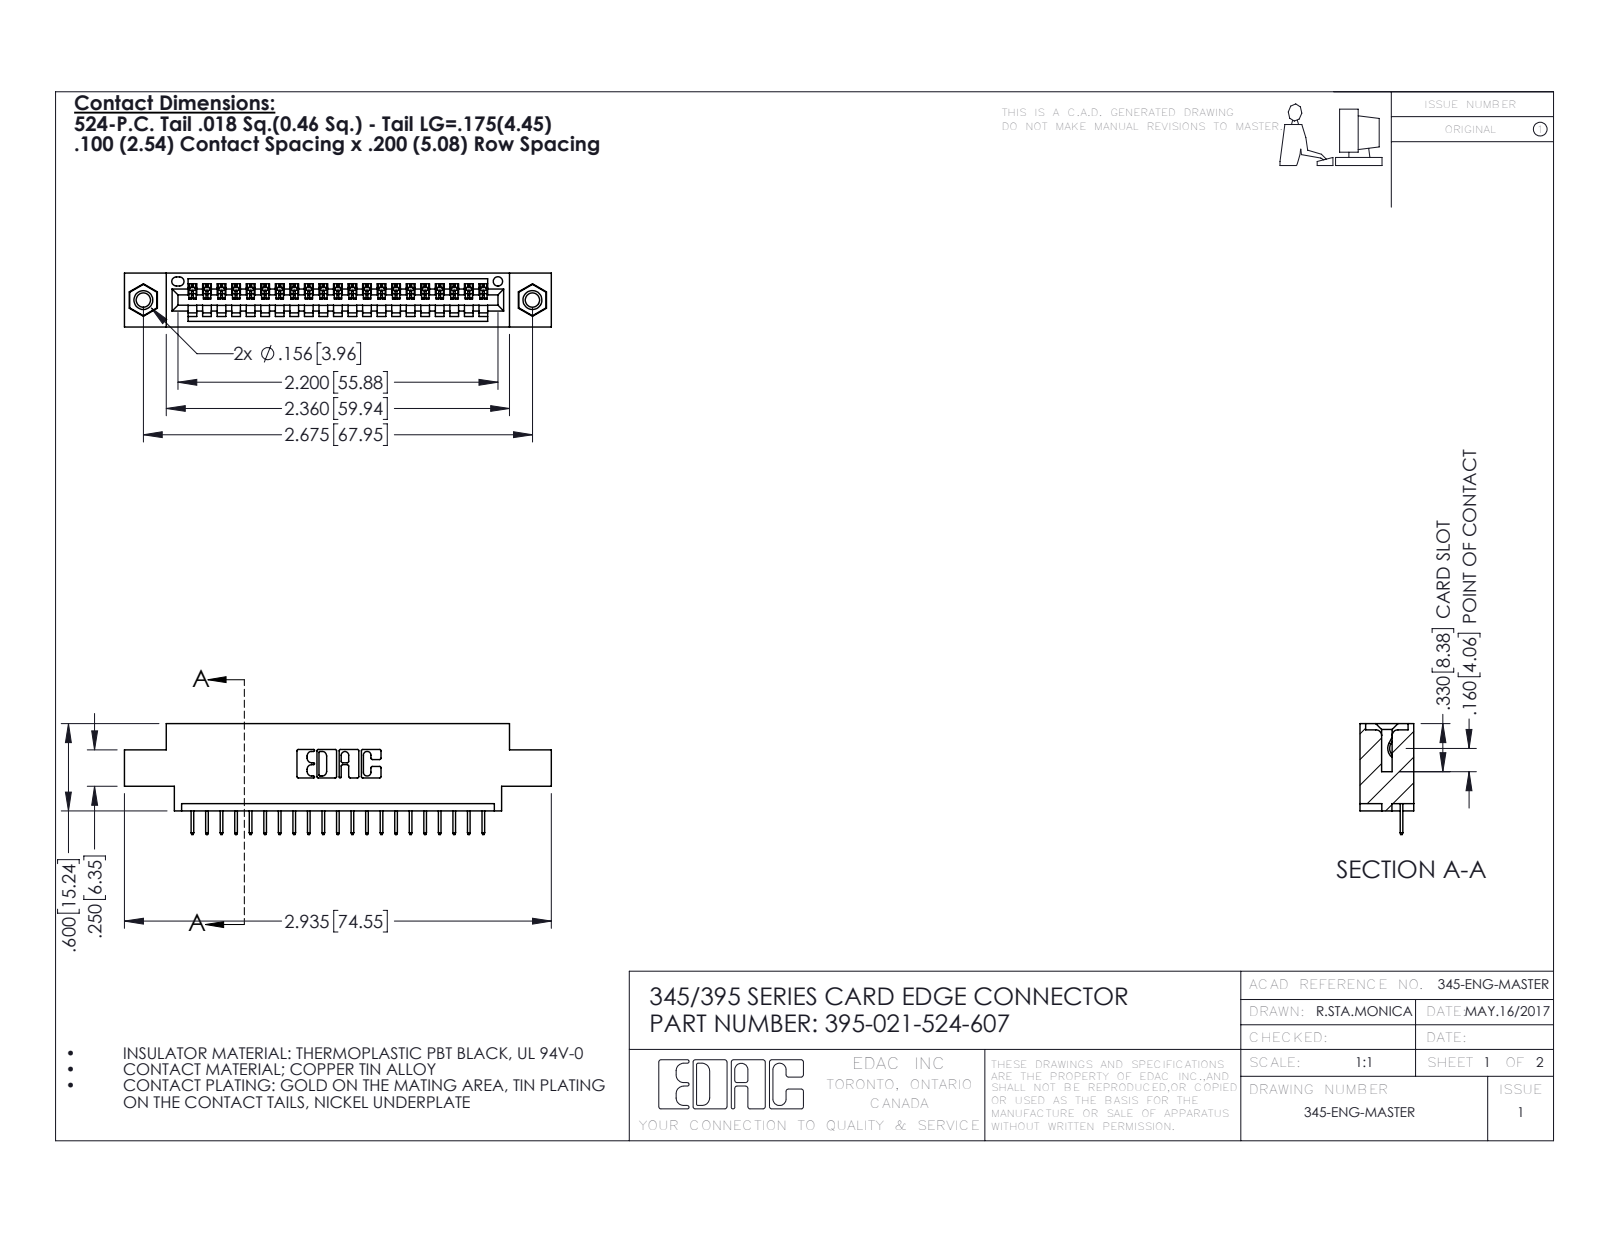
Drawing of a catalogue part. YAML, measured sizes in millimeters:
part_name: "345-250-001_345-250-005-103; 395-021-524-607; 345 Part_0.170 Offset - 0.156 Dia-TI; 345-292-001_345-293-124"
step_written_by: "SolidWorks 2016 (CONFIG_CONTROL_DESIGN)"
units: millimeters
bodies: {solids: 24, faces: 1492, planar: 1082, cylindrical: 394, other: 16}
overall_size: [74.5, 19.4, 9.4]
volume: 6700
surface_area: 8510
round_holes:
  - {diameter: 2.5, count: 2}
  - {diameter: 3.2, count: 2}
  - {diameter: 4, count: 2}
  - {diameter: 1.6, count: 1}
round_bosses_or_shafts:
  - {diameter: 3.9, count: 2}
partial_cylinders:
  - {radius: 0.2, count: 42}
  - {radius: 0.3, count: 22}
  - {radius: 0.2, count: 6}
  - {radius: 0.8, count: 6}
  - {radius: 0.7, count: 3}
  - {radius: 0.8, count: 2}
  - {radius: 1, count: 2}
  - {radius: 0.4, count: 1}
face_to_face_distances: [1.8, 7.6, 9.4, 5.1, 2.5, 6.9, 0.6, 5.7, 1.8, 4.4]
hole_center_spacings: [6.9, 62, 67.9]
